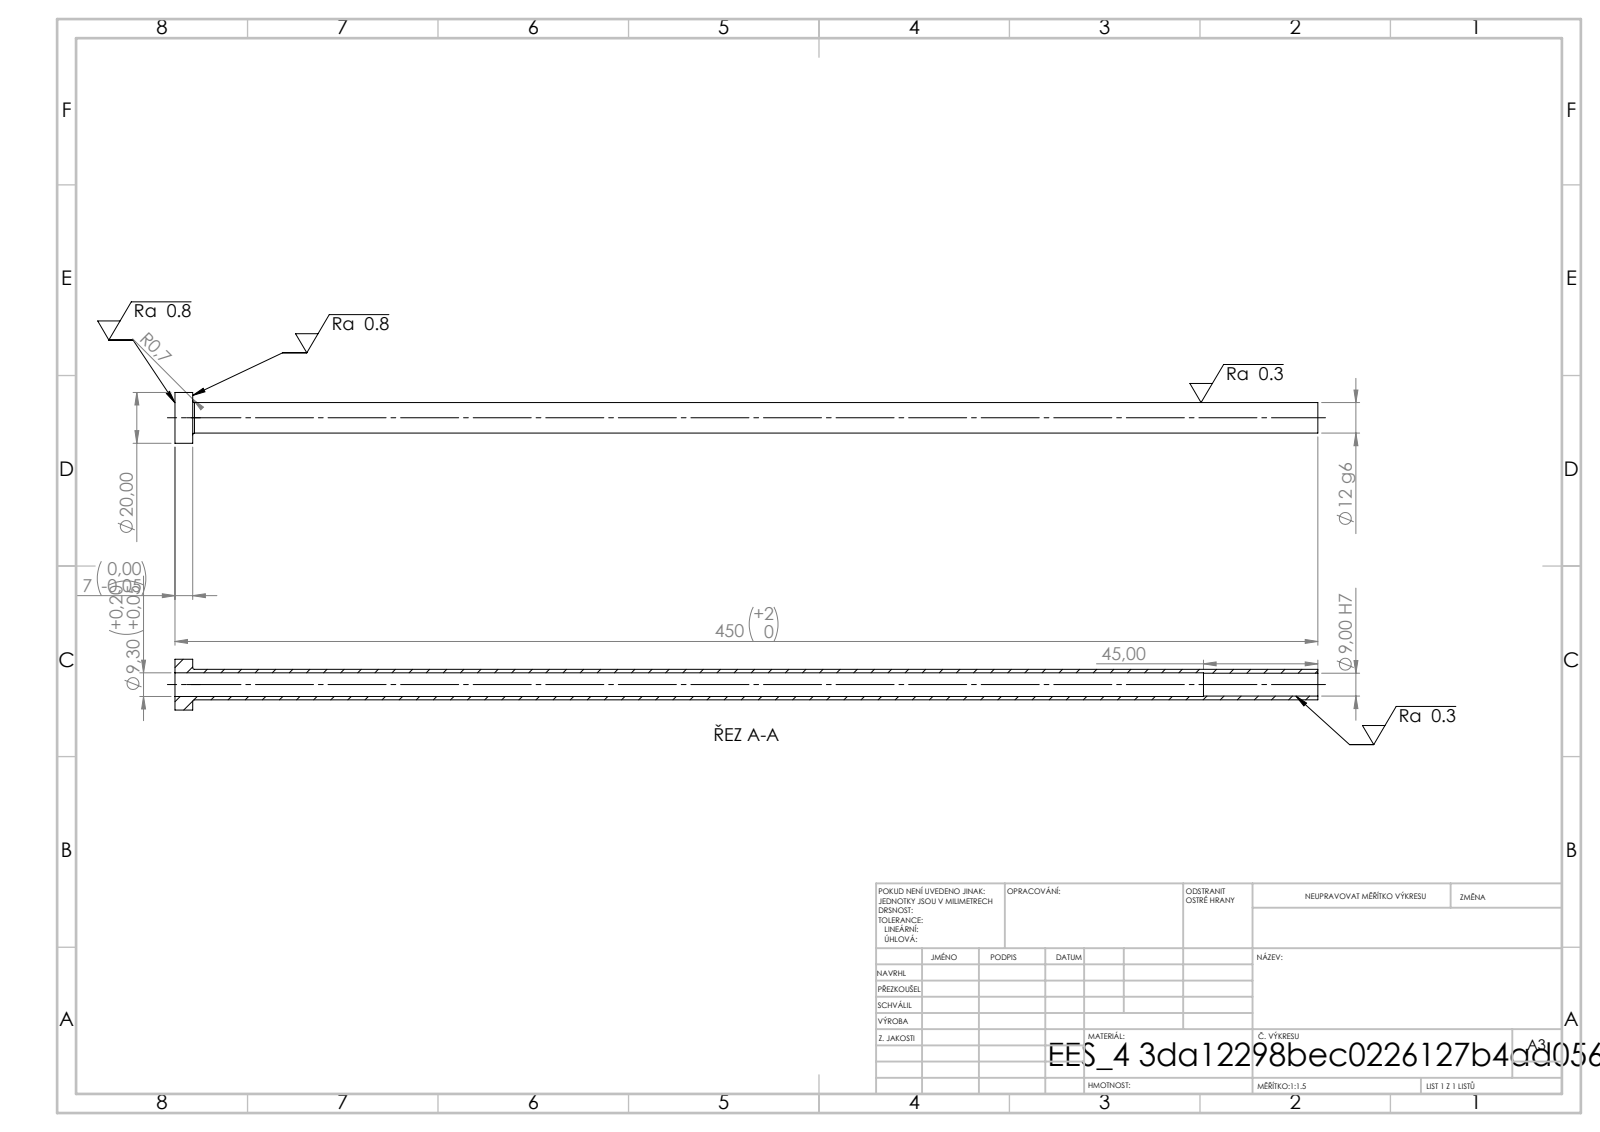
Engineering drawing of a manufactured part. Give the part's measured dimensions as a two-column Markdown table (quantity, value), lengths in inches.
| quantity | value |
| --- | --- |
| STEP written by | SolidWorks 2019 (CONFIG_CONTROL_DESIGN) |
| units | inches |
| bodies | 1 solid, 14 faces (4 planar, 8 cylindrical, 2 other) |
| overall size | 17.717 × 0.787 × 0.787 |
| volume | 1.338 in³ |
| surface area | 47.64 in² |
| round holes (diameter × count) | 0.354 × 1, 0.366 × 1 |
| round bosses / shafts (diameter × count) | 0.787 × 1, 0.472 × 1 |
| main face-to-face distances | 0.276, 17.717, 17.441, 15.945, 15.669, 1.772 |
